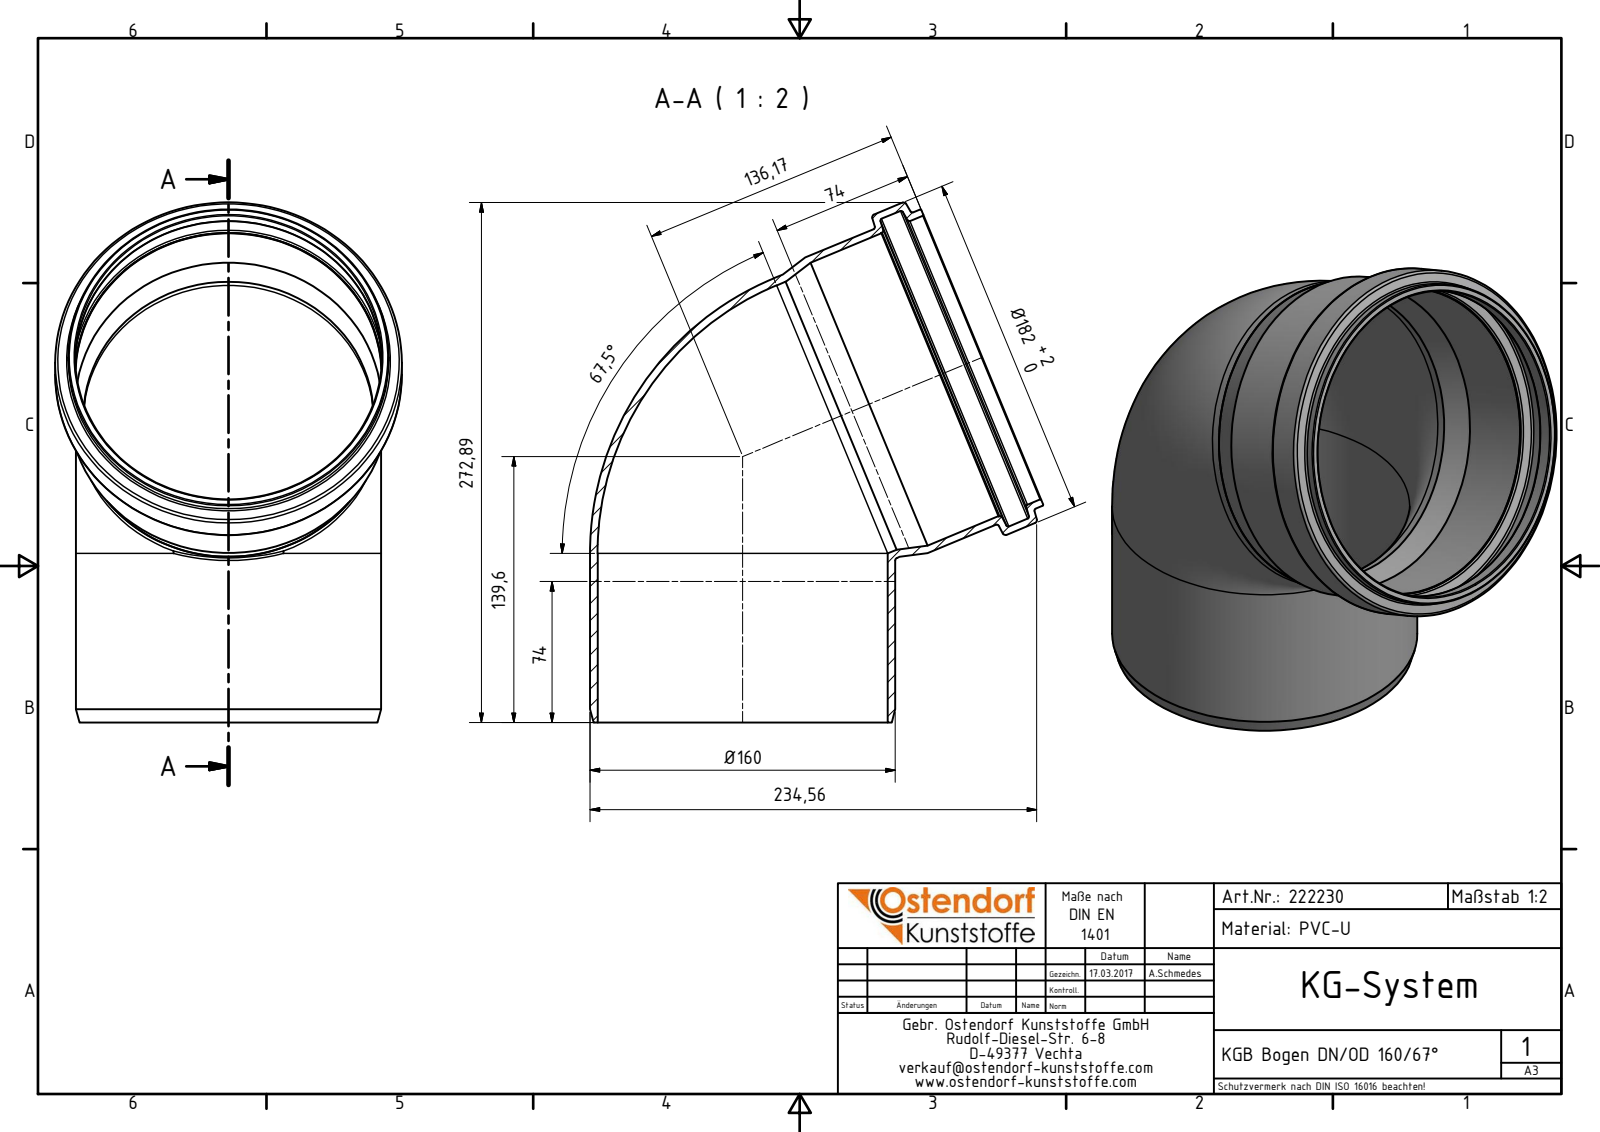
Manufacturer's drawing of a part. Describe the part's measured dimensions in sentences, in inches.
The part is named "222230 KGB Bogen DN_OD 160_67°". Its 3-D file was written by "Autodesk Inventor 2016 (AUTOMOTIVE_DESIGN)". It is 1 solid with 36 faces: 5 planar, 11 cylindrical and 20 other. Overall it measures 10.748 by 9.37 by 7.165 inches. Its volume is 29.1 cubic inches and its surface area 433.2 square inches. Round holes: 2 of diameter 5.996, 2 of diameter 6.343, 1 of diameter 6.327, 1 of diameter 6.882. Round bosses or shafts: 2 of diameter 6.311, 1 of diameter 7.165, 1 of diameter 6.626, 1 of diameter 6.61. The main face-to-face distances are 0.946, 2.21, 3.156, 2.211, 3.157.
